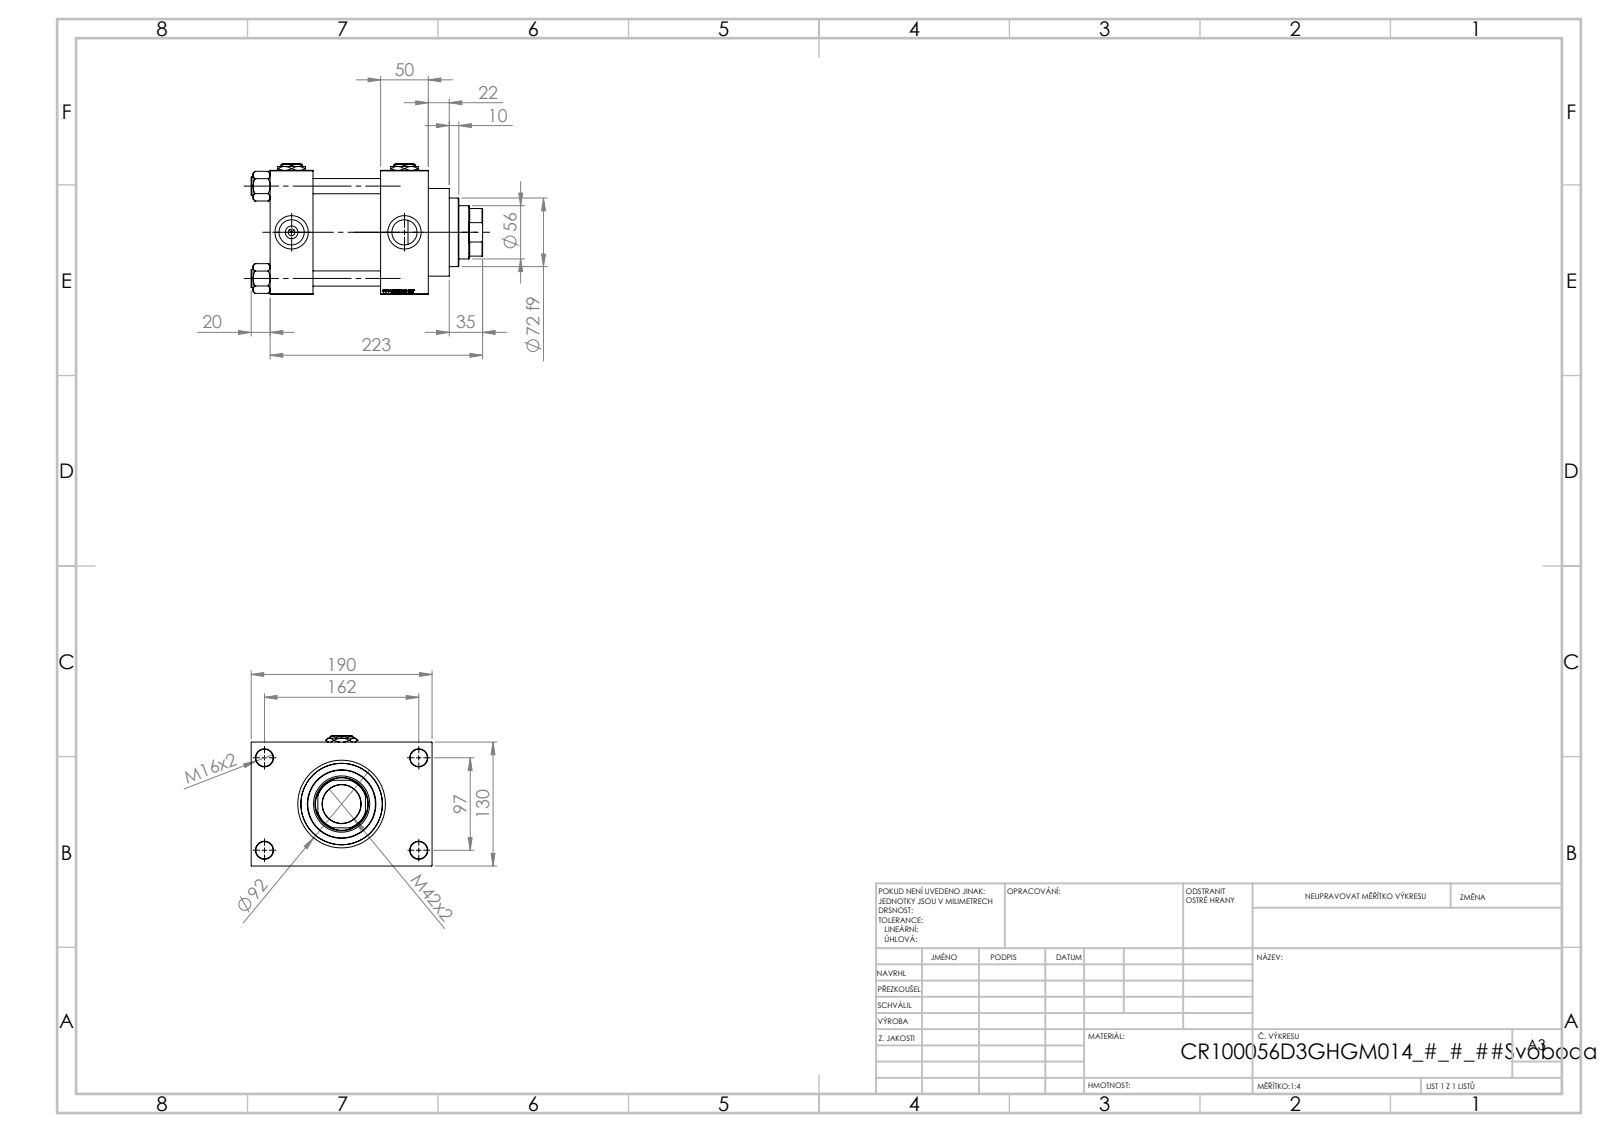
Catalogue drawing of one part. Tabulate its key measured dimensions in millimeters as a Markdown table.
| quantity | value |
| --- | --- |
| part name | V215CR_D_TYCINKA; V215CR_D_Body; Zatka_pro_OIL_PORT; V215CR_VCP_D (+2 more) |
| STEP written by | SolidWorks 2019 (CONFIG_CONTROL_DESIGN) |
| units | millimeters |
| bodies | 13 solids, 1252 faces (593 planar, 99 cylindrical, 560 other) |
| overall size | 243 × 190 × 137 |
| volume | 2 614 000 mm³ |
| surface area | 369 282 mm² |
| round holes (diameter × count) | 16 × 4, 18 × 4, 26.44 × 4, 35 × 4, 7 × 3, 40.5 × 1, 56 × 1, 59 × 1, 76 × 1, 85.5 × 1, 100 × 1 |
| round bosses / shafts (diameter × count) | 19 × 4, 106 × 1, 92 × 1, 72 × 1 |
| partial cylindrical surfaces (radius × count) | 27 × 1 |
| main face-to-face distances | 130, 116, 50, 45, 71, 121, 166, 30, 160, 20 |
| hole center spacings | 32.55, 68.52, 94.41, 96.9, 102.27, 129.45, 161.73, 97 |
